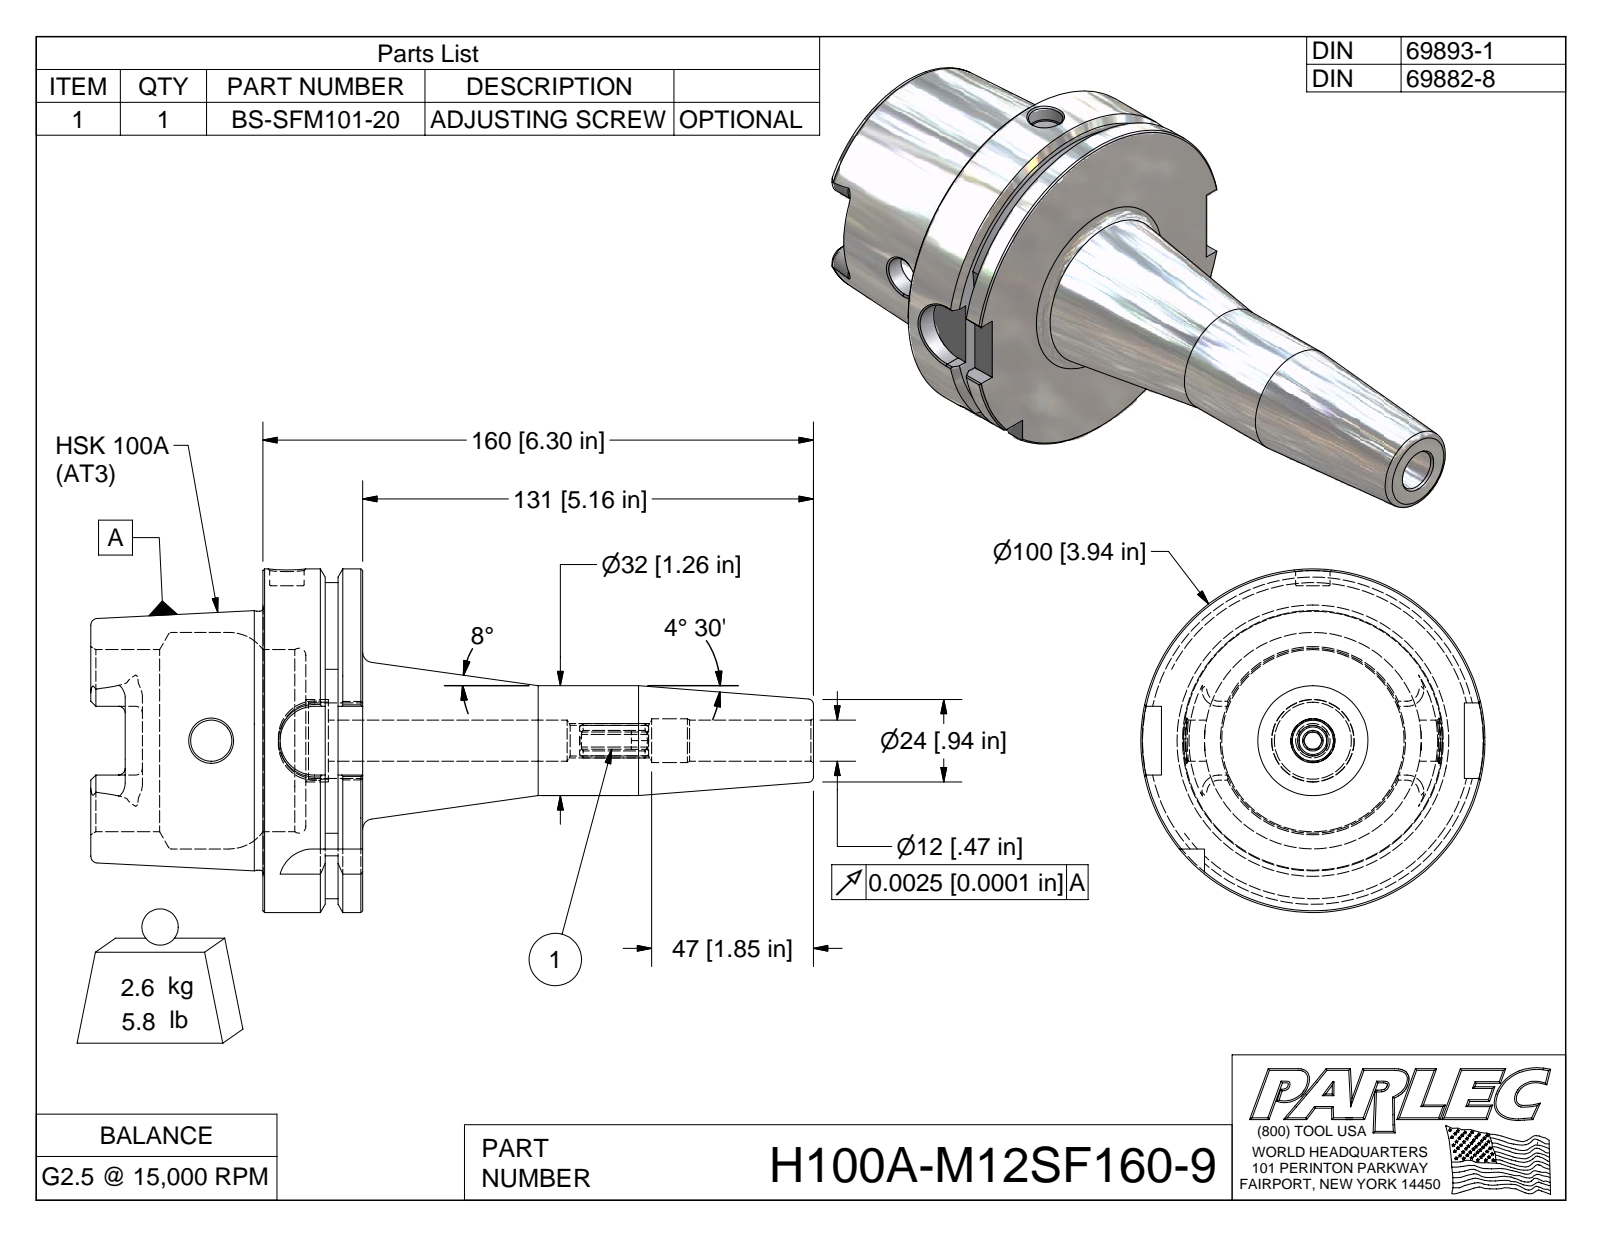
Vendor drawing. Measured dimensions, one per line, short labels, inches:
name: H100A-M12SF160-9; H100A-M12SF160-9-1; BS-SFM101-20
written by: Autodesk Inventor 2009 (AUTOMOTIVE_DESIGN)
unit: in
bodies: 2 solids, 148 faces (48 planar, 29 cylindrical, 71 other)
size: 8.269 × 3.937 × 3.937
volume: 22.04 in³; area: 104.6 in²
holes: 1× ⌀0.394, 1× ⌀0.471, 1× ⌀0.472, 1× ⌀0.501, 1× ⌀0.881, 1× ⌀2.087, 1× ⌀2.48
bosses: 1× ⌀3.937, 1× ⌀2.967, 1× ⌀1.26
rounds: 4× R0.394, 3× R0.079, 2× R0.192, 1× R0.197, 1× R1.811
face distances: 1.142, 0.492, 0.65, 1.969, 2.461, 3.11, 2.682, 0.713, 0.221, 0.428
